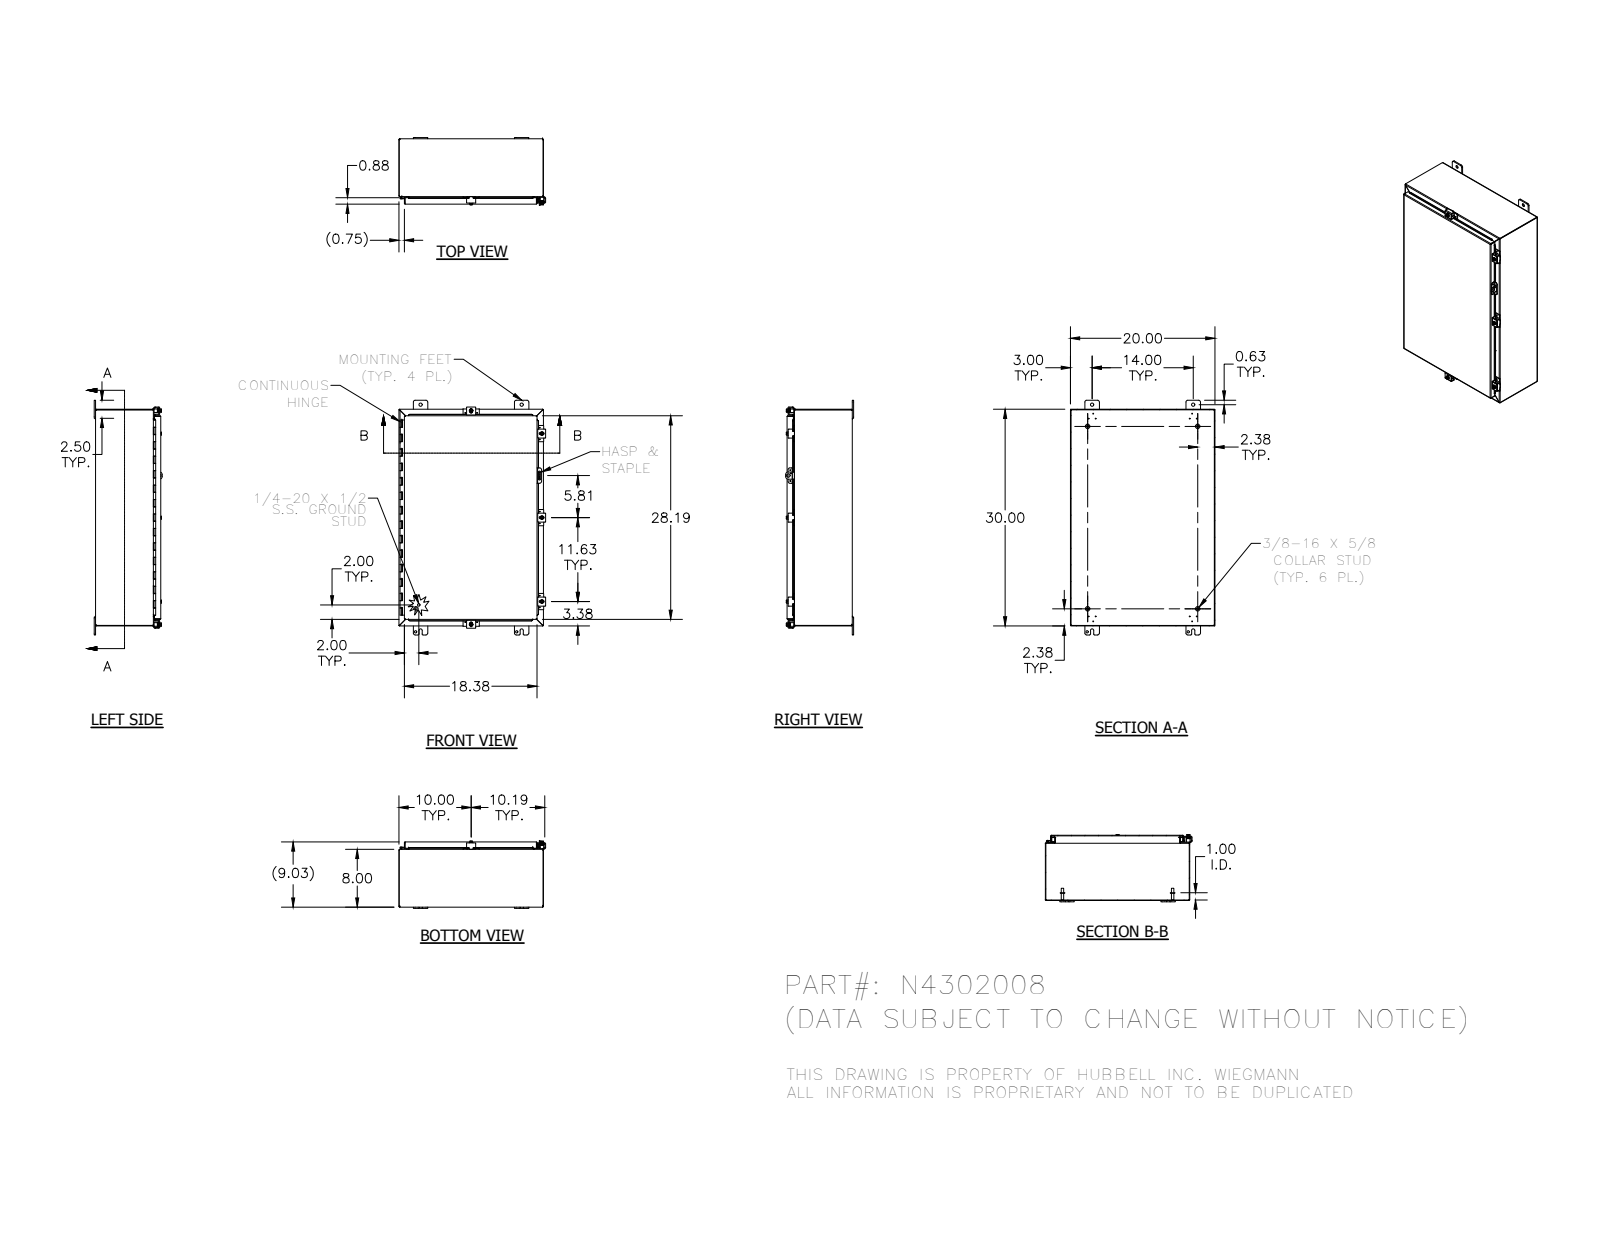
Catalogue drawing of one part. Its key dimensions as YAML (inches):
part_name: "328106T_1; 328106_1; 32911_1; HFW30825-4_1 (+8 more)"
step_written_by: "SolidWorks 2014 (AUTOMOTIVE_DESIGN)"
units: inches
bodies: {solids: 42, faces: 1923, planar: 755, cylindrical: 869, other: 299}
overall_size: [32.5, 20.311, 9.41]
volume: 183.2
surface_area: 4791
round_holes:
  - {diameter: 0.11, count: 13}
  - {diameter: 0.12, count: 12}
  - {diameter: 0.211, count: 5}
  - {diameter: 0.281, count: 5}
  - {diameter: 0.3, count: 5}
  - {diameter: 0.313, count: 4}
  - {diameter: 0.438, count: 4}
  - {diameter: 0.125, count: 1}
  - {diameter: 0.156, count: 1}
  - {diameter: 0.5, count: 1}
round_bosses_or_shafts:
  - {diameter: 0.25, count: 7}
  - {diameter: 0.52, count: 5}
  - {diameter: 0.5, count: 5}
  - {diameter: 0.35, count: 5}
  - {diameter: 0.625, count: 4}
  - {diameter: 0.33, count: 4}
  - {diameter: 0.115, count: 2}
  - {diameter: 0.337, count: 1}
partial_cylinders:
  - {radius: 0.03, count: 61}
  - {radius: 0.125, count: 35}
  - {radius: 0.062, count: 31}
  - {radius: 0.25, count: 31}
  - {radius: 0.031, count: 23}
  - {radius: 0.105, count: 23}
  - {radius: 0.063, count: 14}
  - {radius: 0.141, count: 10}
face_to_face_distances: [0.074, 8.959, 8.885, 9.033, 19.926, 29.926, 7.926, 1.033, 19.852, 20]
hole_center_spacings: [14, 0.876, 0.759, 0.839, 0.94, 0.969, 1.593, 1.995]
